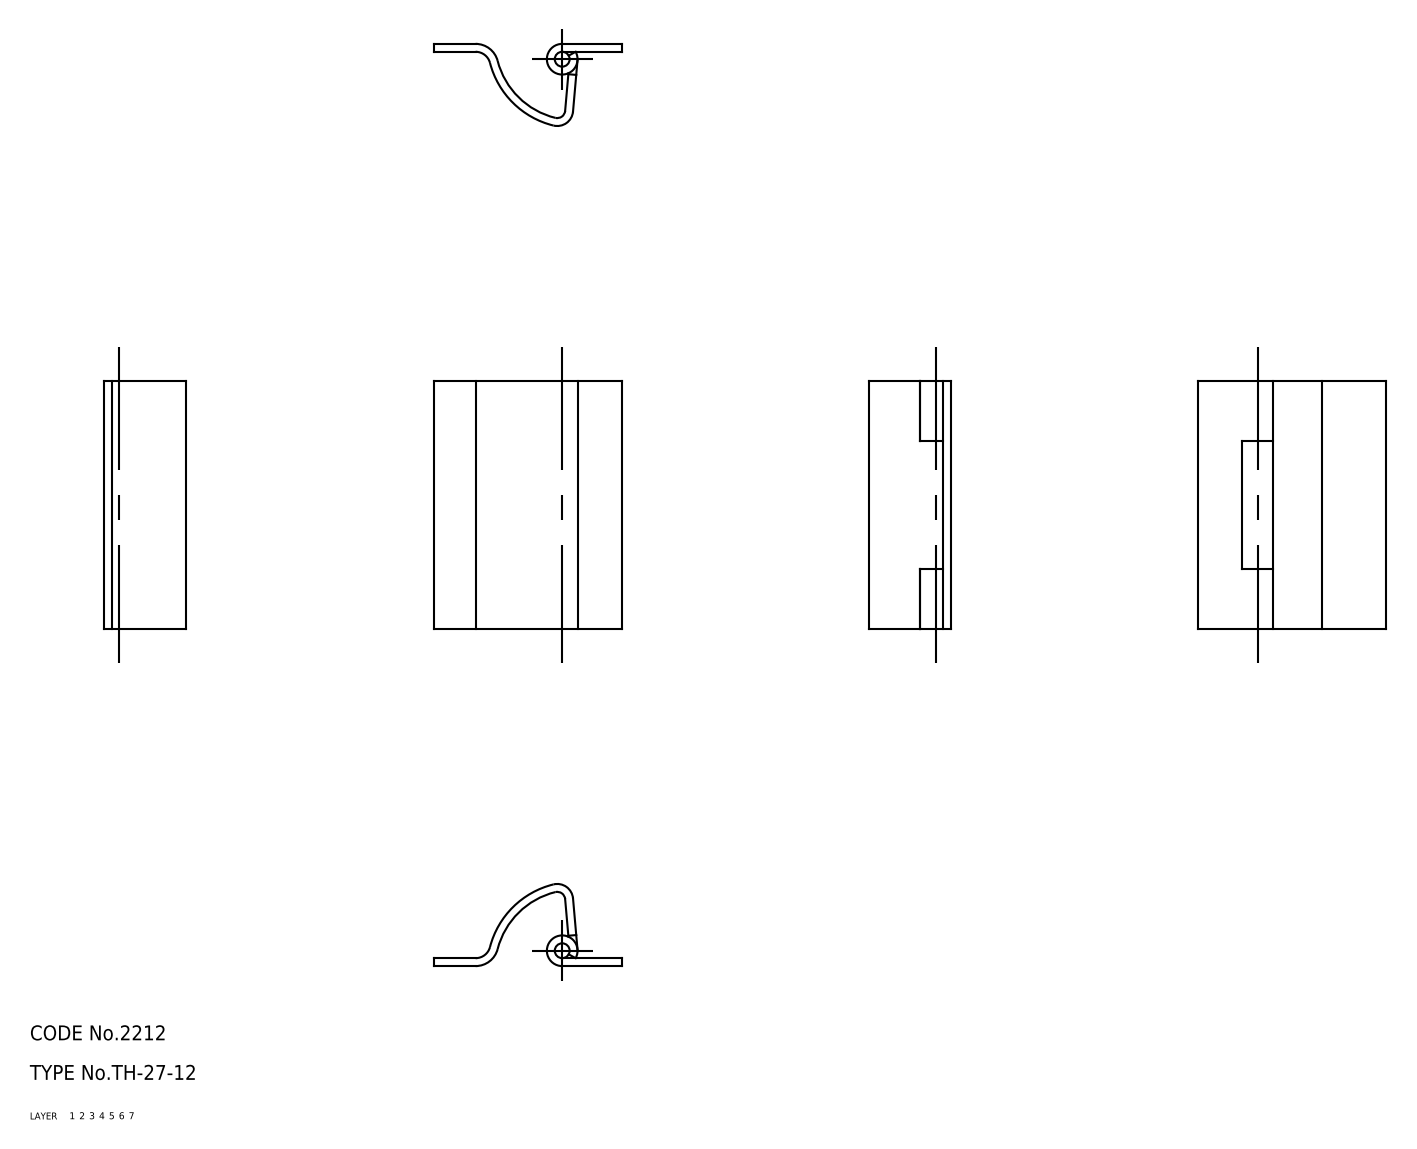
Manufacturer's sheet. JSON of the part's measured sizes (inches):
{"part_name": "shaft; hinge piece_B; hinge piece_A; TH_27_12_6763_36", "step_written_by": "CADfix (AUTOMOTIVE_DESIGN)", "units": "inches", "bodies": {"solids": 3, "faces": 38, "planar": 0, "cylindrical": 0, "other": 38}, "overall_size": [1.969, 1.496, 0.654], "volume_in3": 0.349, "surface_area_in2": 12.12}
